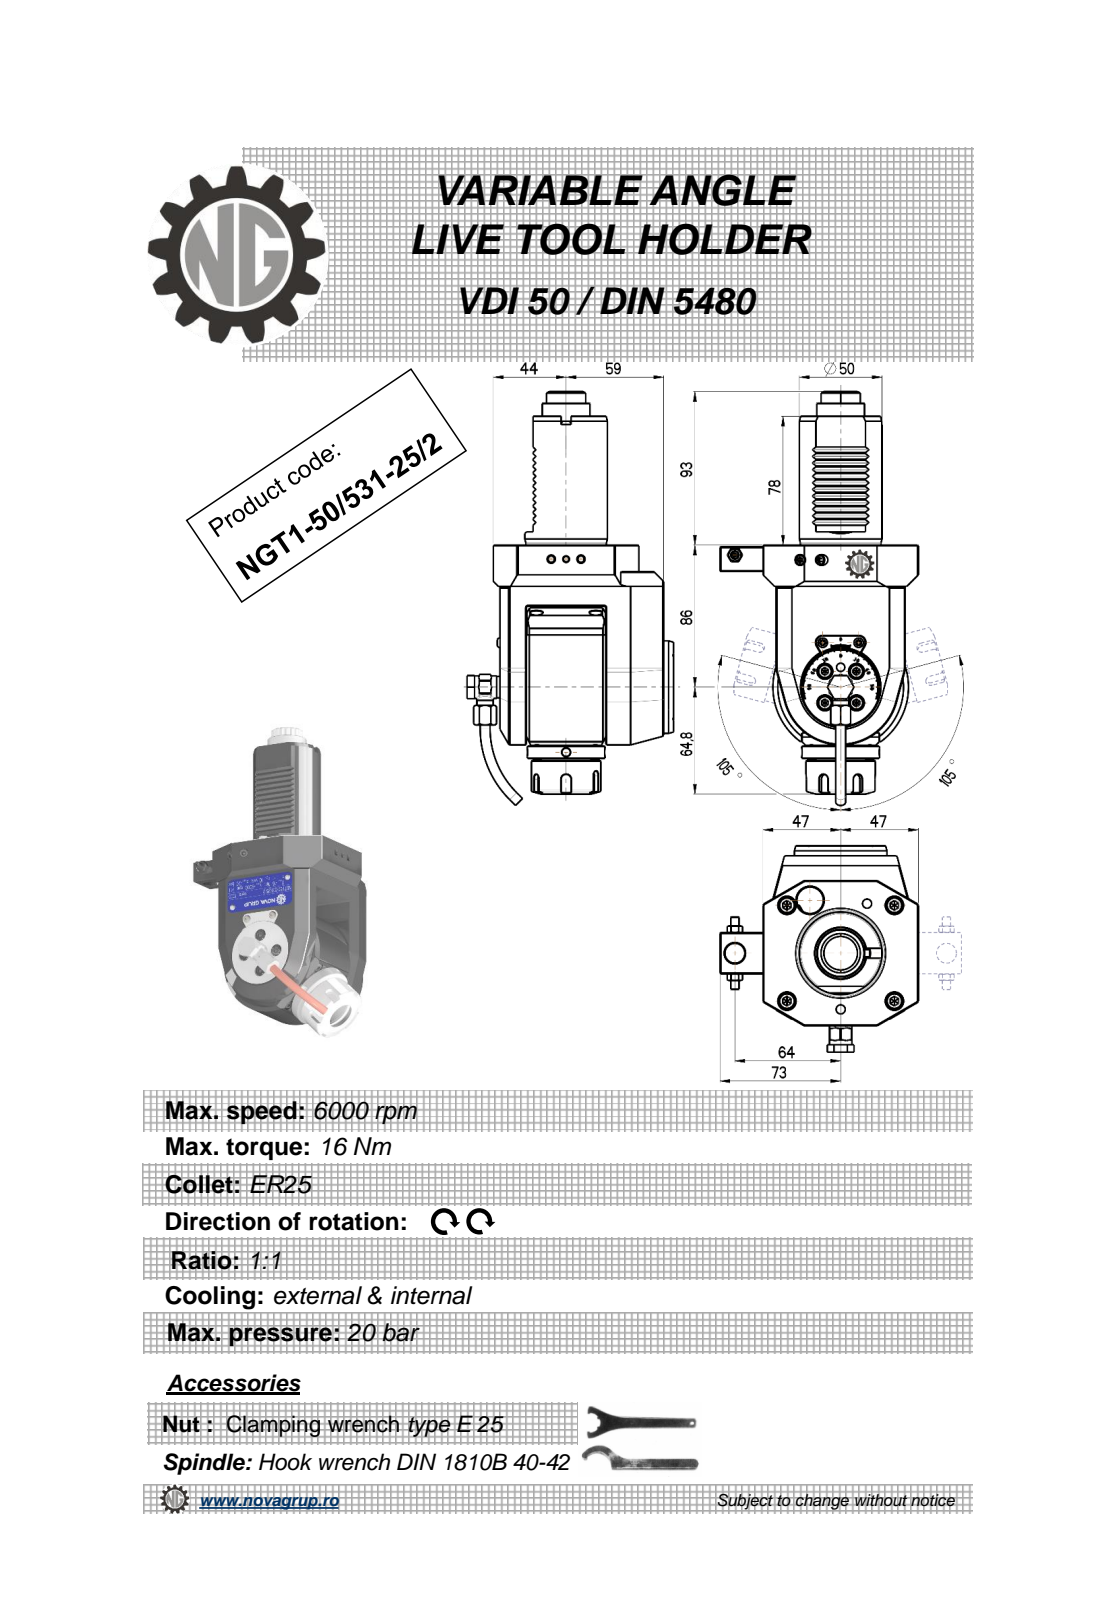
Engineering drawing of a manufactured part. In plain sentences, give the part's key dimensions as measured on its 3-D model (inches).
The part is named "NGT1_50_531_25_2". Its 3-D file was written by "PRO/ENGINEER BY PARAMETRIC TECHNOLOGY CORPORATION, 2010280 (CONFIG_CONTROL_DESIGN)". It is 1 solid with 712 faces: 271 planar, 211 cylindrical and 230 other. Overall it measures 9.869 by 4.917 by 4.724 inches. Its volume is 63.59 cubic inches and its surface area 141.5 square inches. Round holes: 3 of diameter 0.157, 2 of diameter 0.197, 1 of diameter 0.118, 1 of diameter 0.165, 1 of diameter 0.244, 1 of diameter 0.354, 1 of diameter 0.374, 1 of diameter 0.394, 1 of diameter 0.433, 1 of diameter 0.472, 1 of diameter 0.799. Round bosses or shafts: 2 of diameter 0.236, 2 of diameter 0.224, 1 of diameter 2.205, 1 of diameter 1.969, 1 of diameter 1.85, 1 of diameter 1.654, 1 of diameter 1.378, 1 of diameter 1.134. Partial cylindrical surfaces (rounded edges, fillets, slot ends): 36 of radius 0.12, 12 of radius 0.01, 12 of radius 0.012, 6 of radius 0.006, 5 of radius 0.118, 4 of radius 0.02, 2 of radius 0.039, 2 of radius 0.394. The main face-to-face distances are 1.457, 3.898, 3.071, 0.315, 0.63, 0.787, 0.236, 2.52, 4.134, 0.827. The hole center spacings are 0.016, 1.553, 1.929, 1.945, 2.52, 3.173, 3.183, 4.033.
